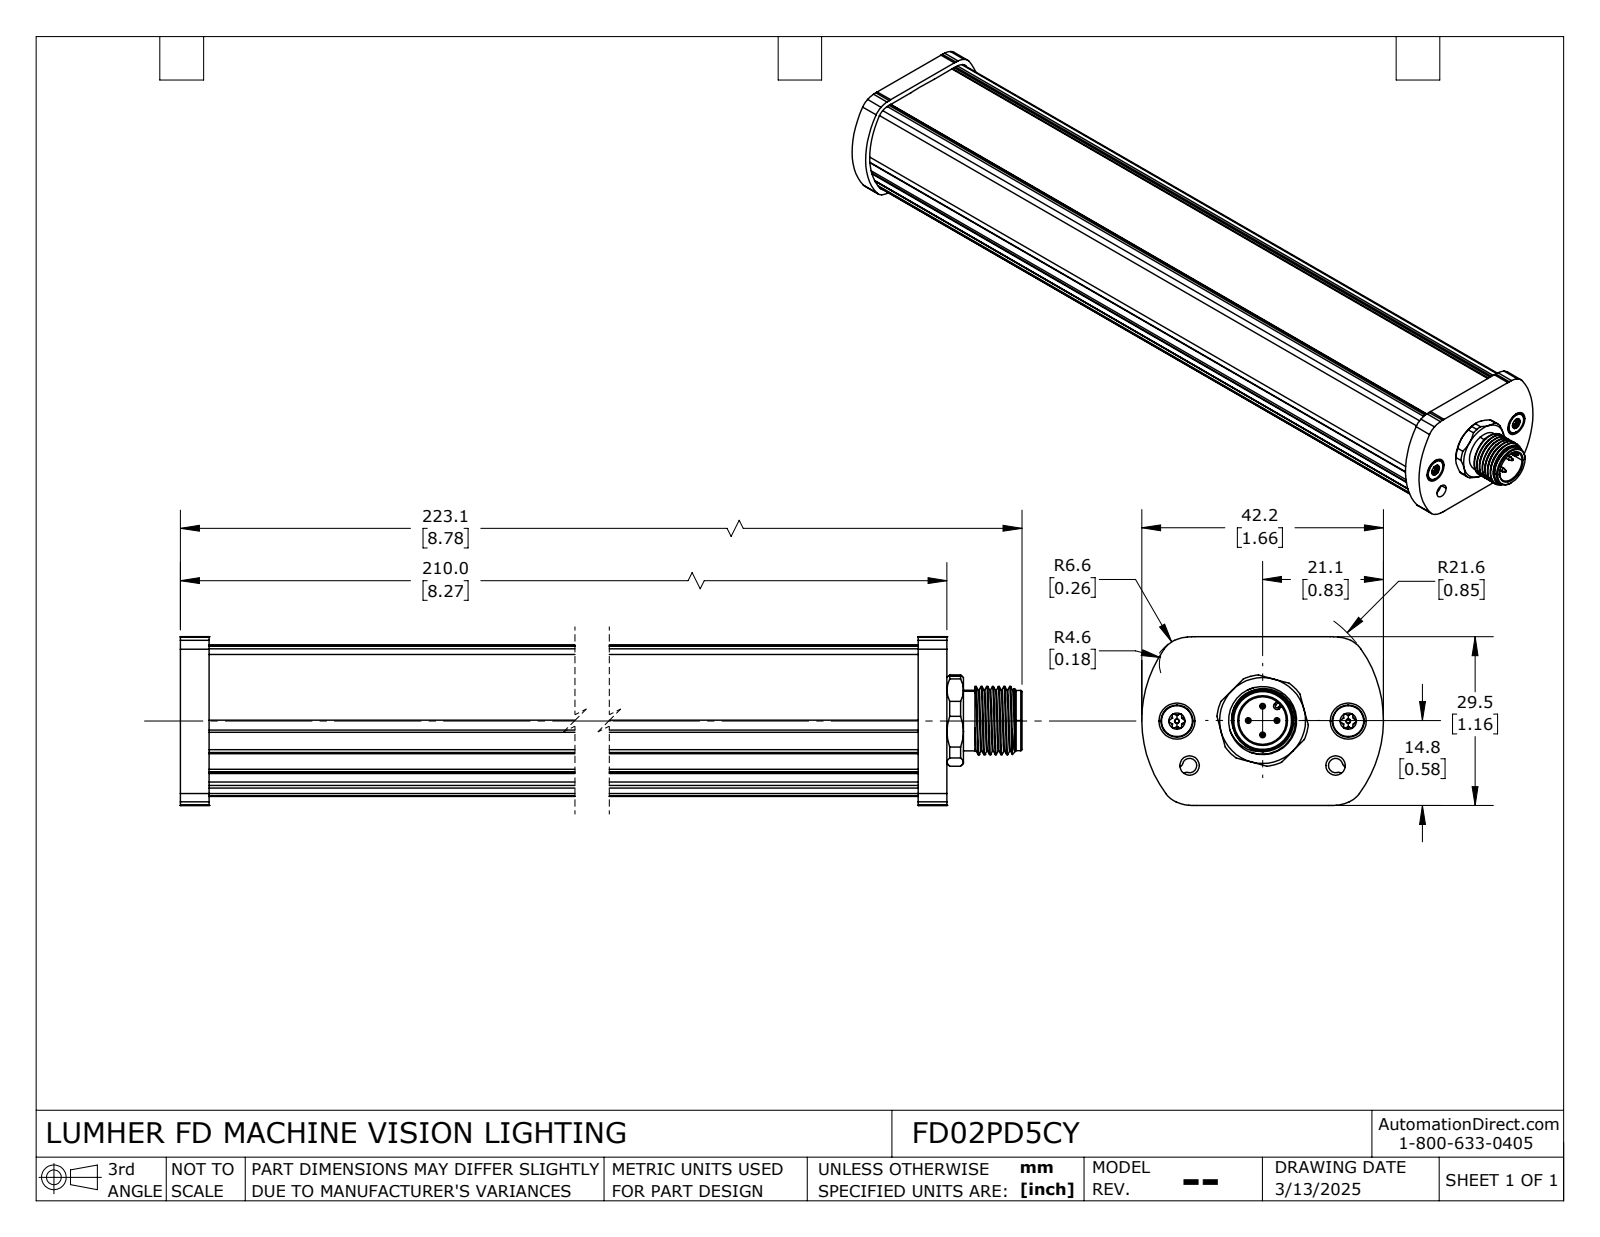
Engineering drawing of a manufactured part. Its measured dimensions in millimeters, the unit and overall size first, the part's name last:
Units: millimetres
Overall size (bounding box): 223.1 × 42.21 × 29.45
Round holes (diameter × count): ⌀1.45 ×4, ⌀3.4 ×4, ⌀8.3 ×1, ⌀9 ×1, ⌀9.4 ×1
Round bosses / shafts (diameter × count): ⌀1.4 ×4, ⌀1 ×4, ⌀5.6 ×2, ⌀3 ×2, ⌀0.8 ×2, ⌀11.9 ×1, ⌀10.6 ×1, ⌀10.5 ×1
Partial cylindrical surfaces — rounded edges, fillets, slot ends (radius × count): R0.57 ×24, R0.25 ×12, R0.8 ×12, R3 ×10, R0.3 ×4, R1.25 ×4, R3.1 ×4, R4.6 ×4
Main face-to-face distances: 2.5, 5, 7.5, 10, 12.5, 2, 4, 3, 205, 208
Hole centre spacings: 2.5, 3.54, 14.96, 5, 8.06, 12.46, 12.91, 13.83
Volume: 179 320 mm³ · Surface area: 48 983 mm²
Bodies: 1 solid, 662 faces (97 planar, 383 cylindrical, 182 other)
Part name (STEP PRODUCT): FD02PD5CY
STEP written by: SolidWorks 2024 (AUTOMOTIVE_DESIGN)
